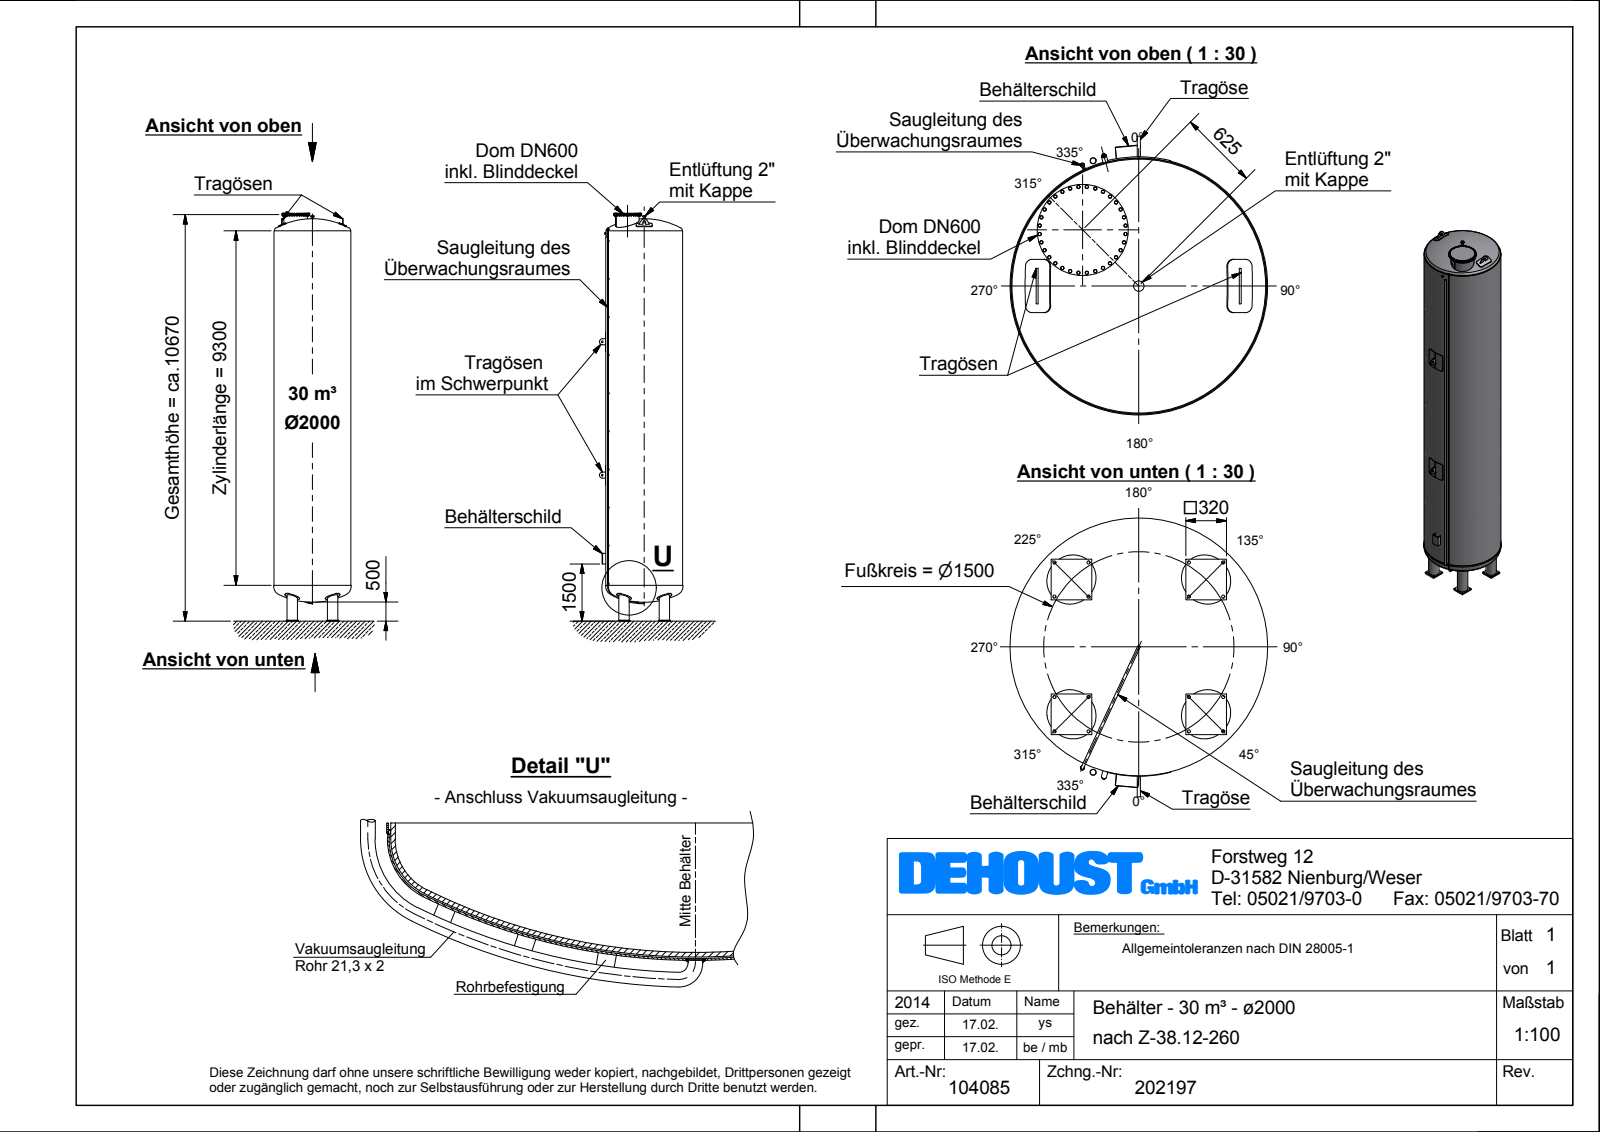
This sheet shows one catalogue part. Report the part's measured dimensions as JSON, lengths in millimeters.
{"part_name": "Z-38_12-260_Beh\\S\\dlter_\\S\\x2000_030m\\S\\3_Dichte=1,0", "step_written_by": "Autodesk Inventor 2012 (AUTOMOTIVE_DESIGN)", "units": "millimeters", "bodies": {"solids": 14, "faces": 1232, "planar": 746, "cylindrical": 158, "other": 328}, "overall_size": [10699.18, 2195, 2030], "volume_mm3": 30770000000, "surface_area_mm2": 83120000, "round_holes": [[257, 4], [598, 1], [1988, 1]], "round_bosses_or_shafts": [[22.5, 32], [16, 32], [400, 4], [273, 4], [21.3, 2], [2030, 1], [2016, 1], [2000, 1]], "partial_cylinders_radius": [[50, 8], [56, 8], [80, 2], [35, 1], [85, 1], [1018, 1]], "face_to_face_distances": [25, 10242.2, 10689.17, 446.97, 10654.17, 411.97, 35, 10217.2, 10629.17, 10664.17], "hole_center_spacings": [750, 1060.66, 976.28, 1500, 125, 625, 1375]}
